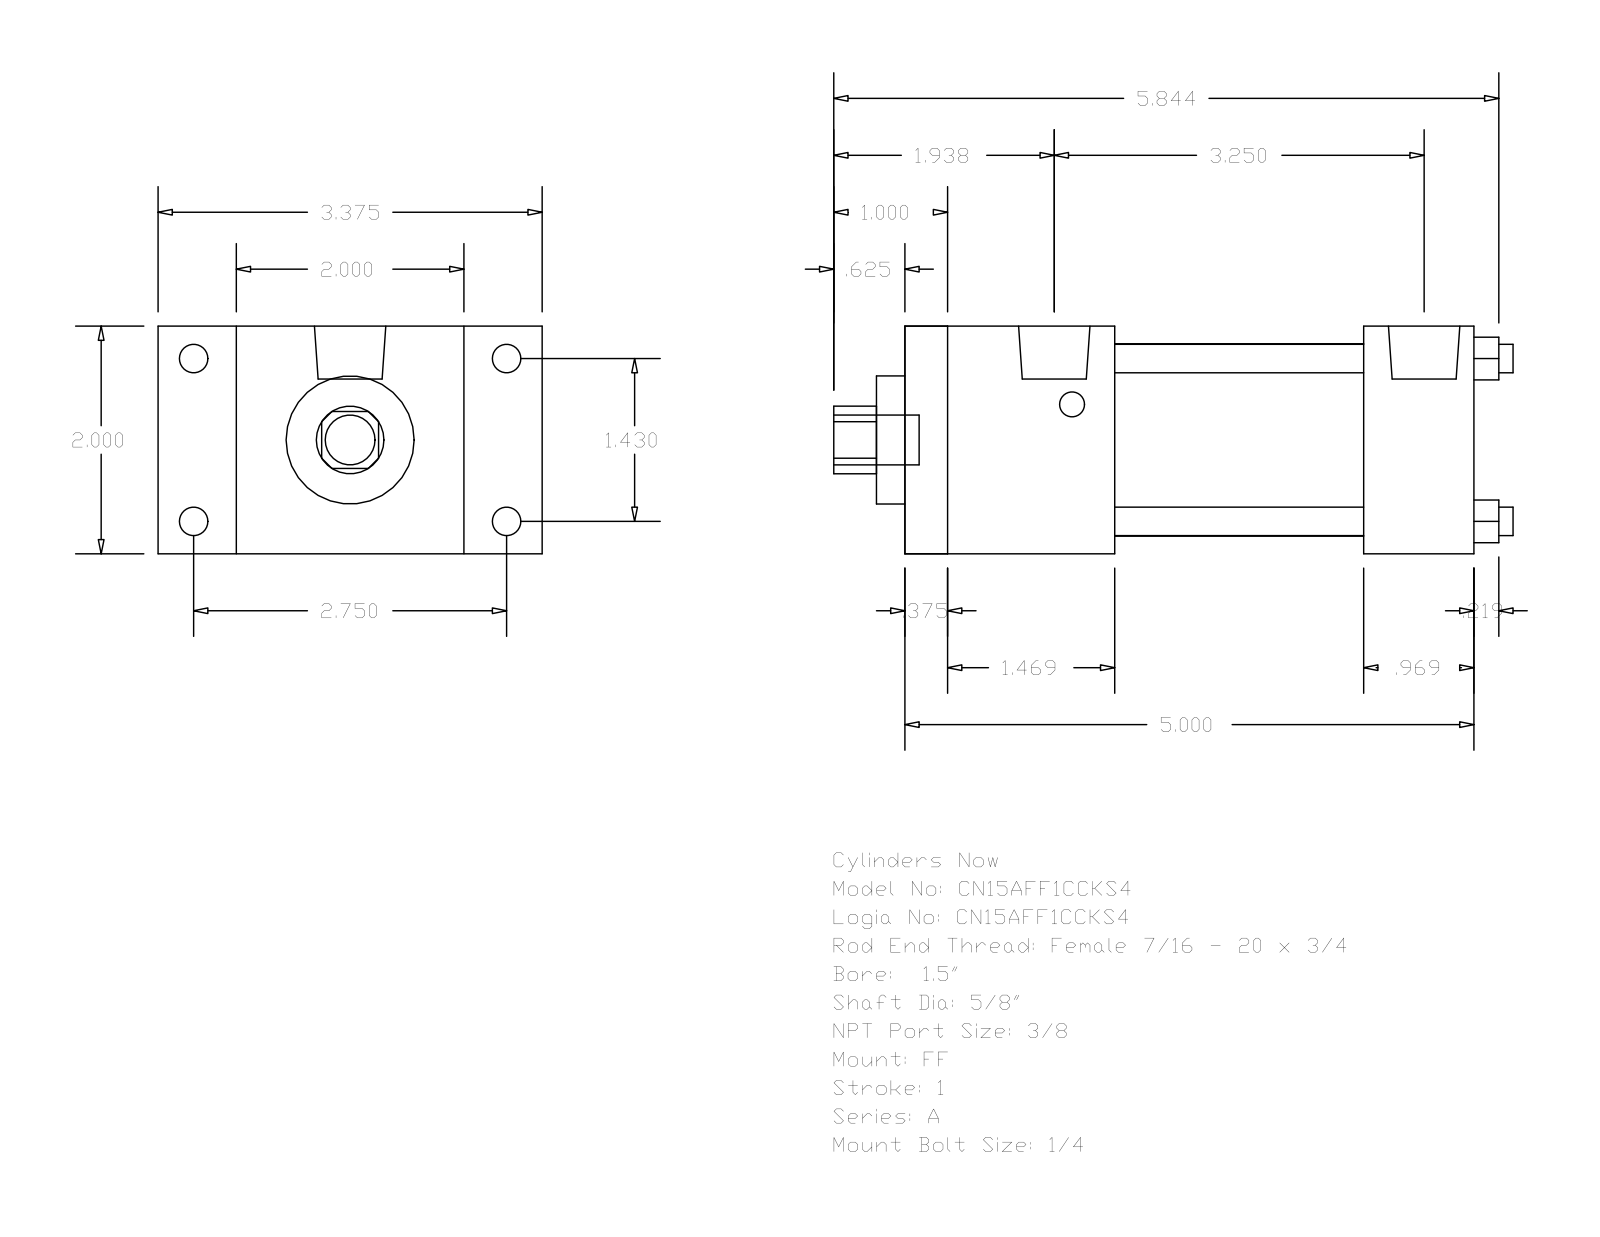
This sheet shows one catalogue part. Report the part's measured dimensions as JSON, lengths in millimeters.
{"part_name": "A_FF__0150_0.625", "step_written_by": "GSSL Pune (CONFIG_CONTROL_DESIGN)", "units": "millimeters", "bodies": {"solids": 0, "faces": 92, "planar": 64, "cylindrical": 28, "other": 0}, "overall_size": [151.61, 85.72, 50.8], "round_holes": [[6.35, 4], [15.88, 1], [28.57, 1], [42.93, 1]], "round_bosses_or_shafts": [[6.35, 4], [5.56, 4], [15.93, 2], [11.11, 1]], "partial_cylinders_radius": [[7.54, 1]], "face_to_face_distances": [50.8, 127, 9.52, 117.48, 46.83, 102.39, 37.31, 92.87, 55.56, 80.17], "hole_center_spacings": [25.68, 36.32, 51.36]}
